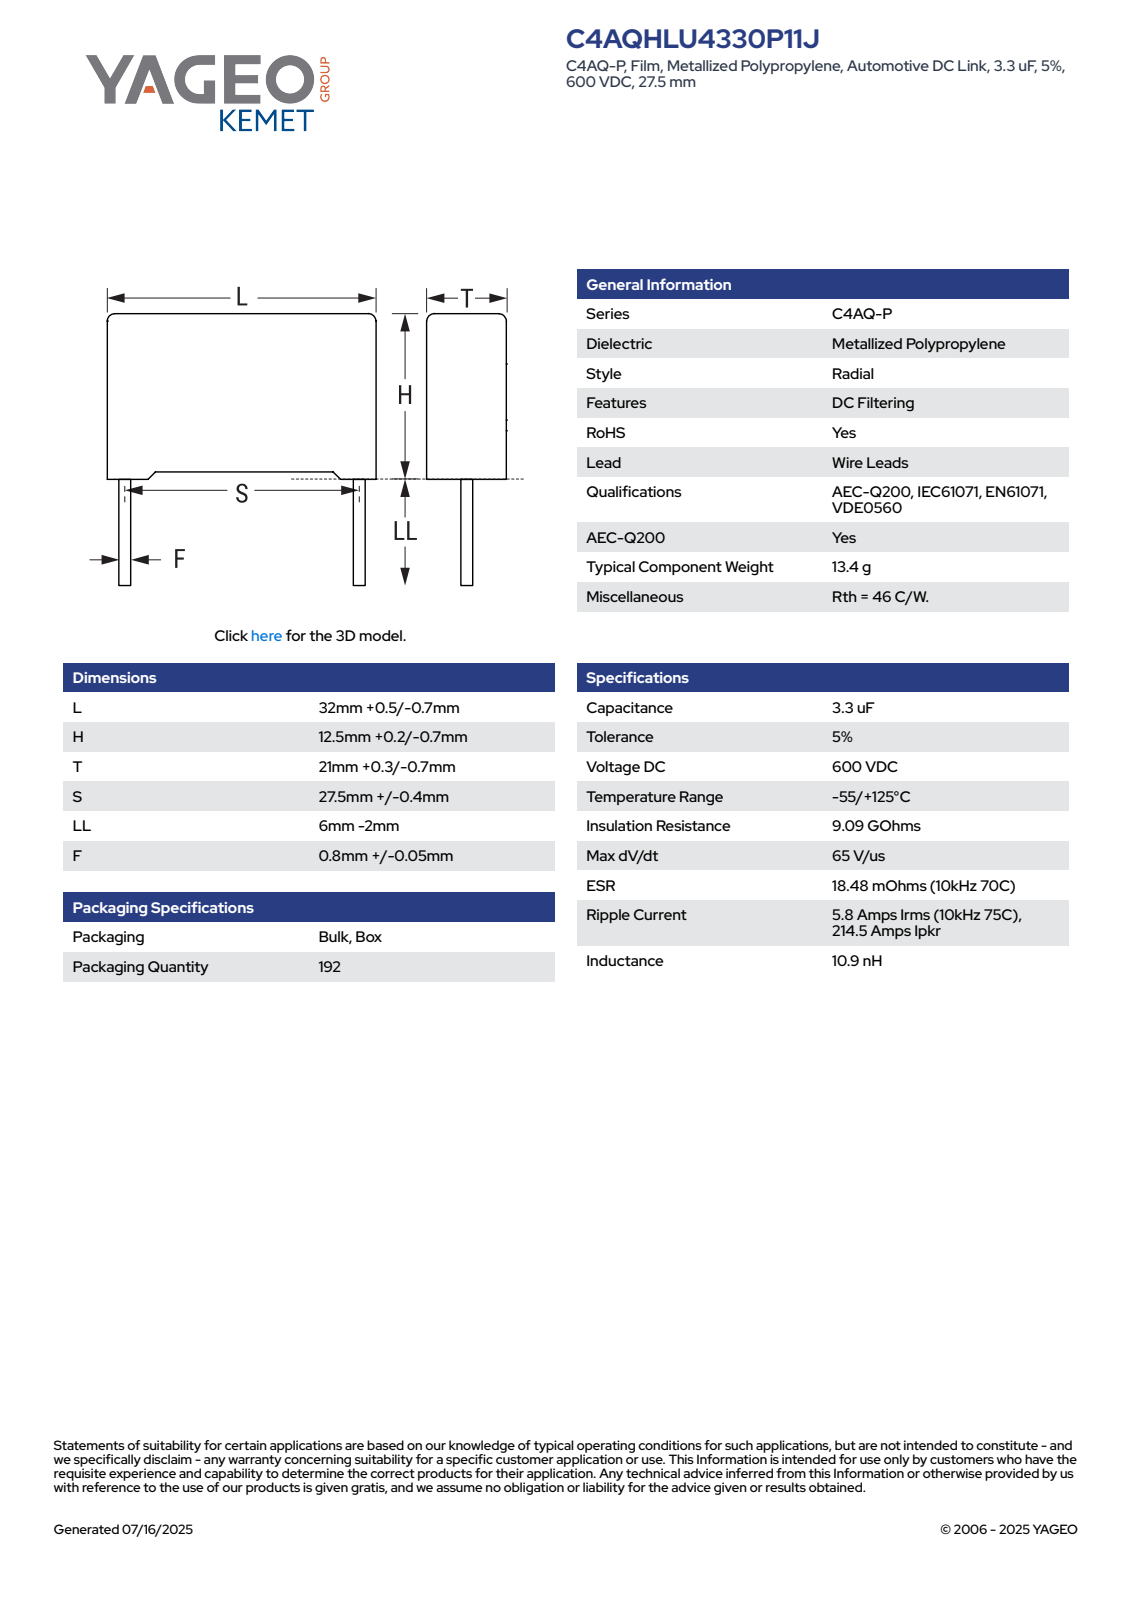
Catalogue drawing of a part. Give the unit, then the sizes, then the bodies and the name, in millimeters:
Units: millimetres
Overall size (bounding box): 32.5 × 21.3 × 16.7
Round bosses / shafts (diameter × count): ⌀0.85 ×2
Partial cylindrical surfaces — rounded edges, fillets, slot ends (radius × count): R0.5 ×4
Main face-to-face distances: 11.95, 21.3, 32.5, 0.75, 12.7, 1.08, 0.44, 0.31, 12.26, 31.42
Volume: 8 334 mm³ · Surface area: 2 866 mm²
Bodies: 4 solids, 85 faces (77 planar, 8 cylindrical, 0 other)
Part name (STEP PRODUCT): CFR_RB2CFP_32X12.5X21_L32.5H12.7T21.3S27.5LL4F0.85
STEP written by: SolidWorks 2014 (AUTOMOTIVE_DESIGN)
